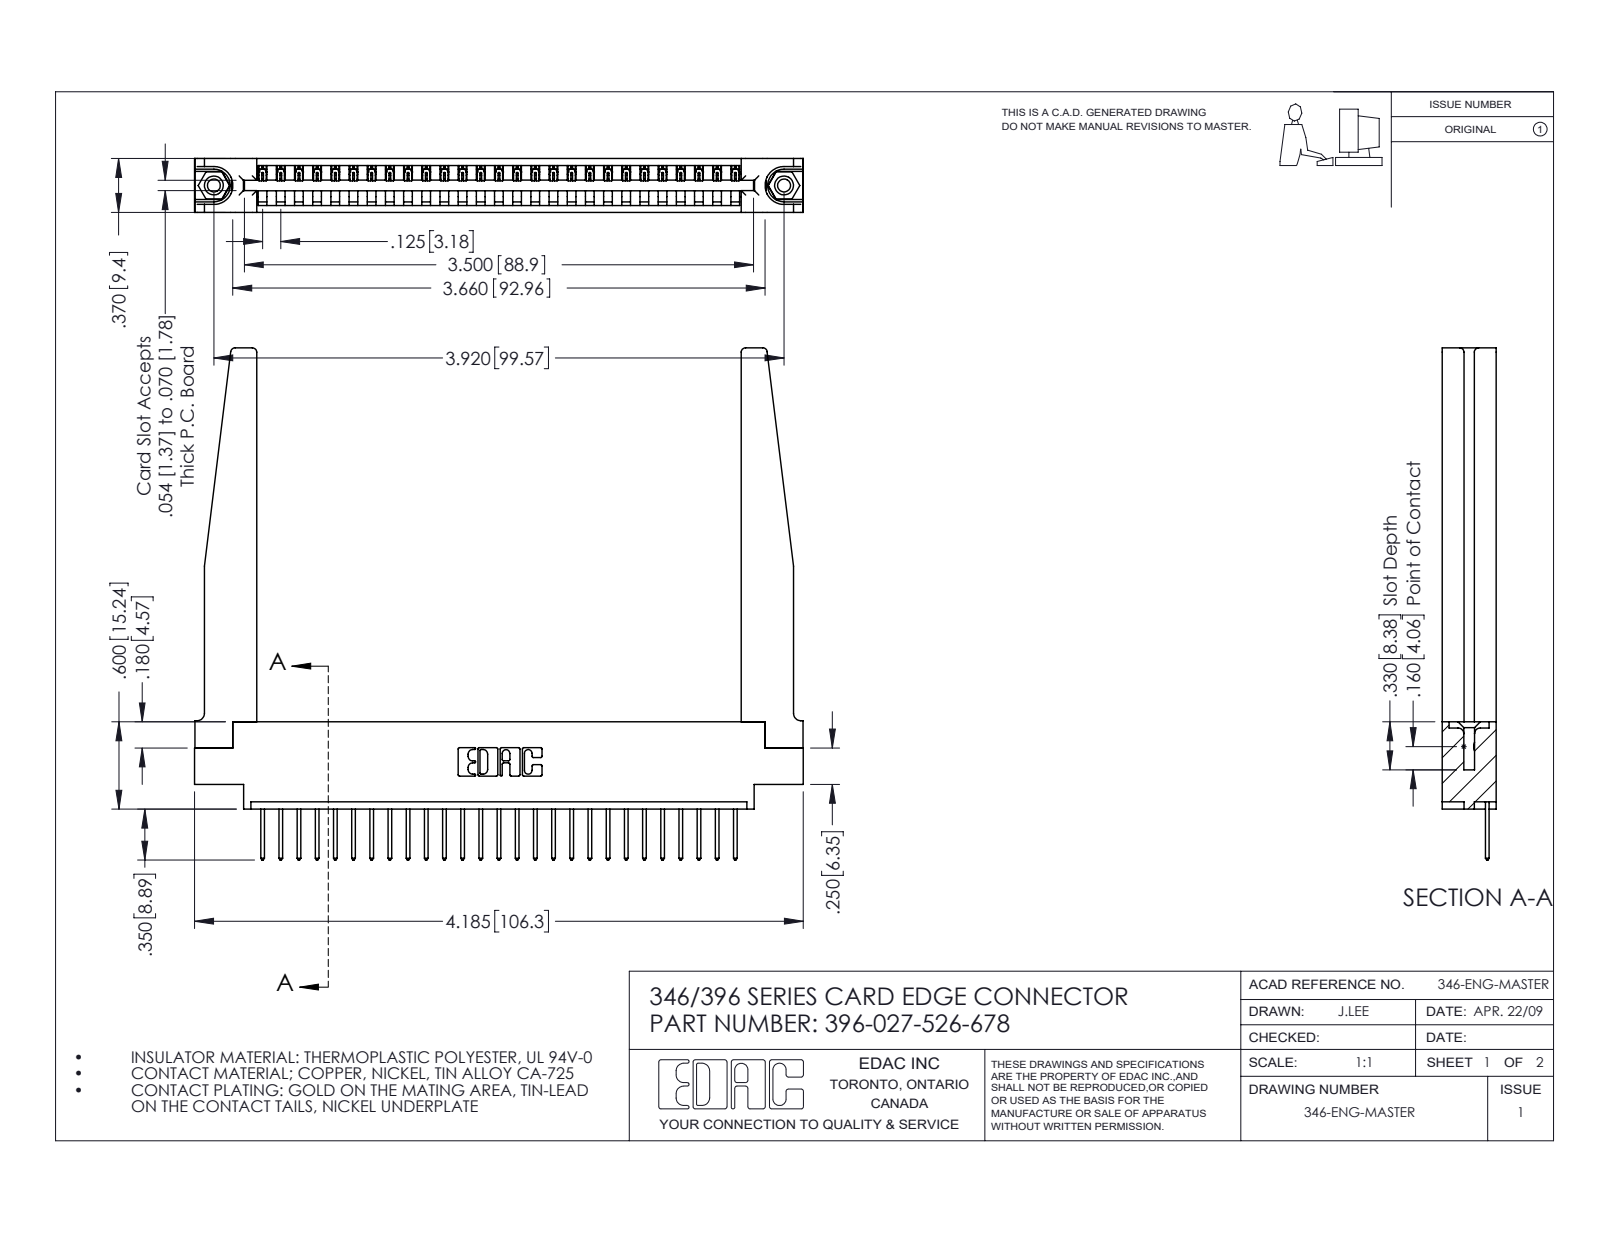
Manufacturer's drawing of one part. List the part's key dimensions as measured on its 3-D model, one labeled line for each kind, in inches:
Part name (STEP PRODUCT): 345-250-001_345-250-001-102; 396-027-526-678; 346-220-078_345-220-078; 346 Part_0.170 Offset - 0.156 Dia-TH (+1 more)
STEP written by: SolidWorks 2016 (CONFIG_CONTROL_DESIGN)
Units: inches
Bodies: 32 solids, 1926 faces (1302 planar, 572 cylindrical, 52 other)
Overall size (bounding box): 4.185 × 3.52 × 0.37
Volume: 1.025 in³ · Surface area: 29.27 in²
Round holes (diameter × count): ⌀0.089 ×2, ⌀0.125 ×2, ⌀0.156 ×2, ⌀0.064 ×1
Round bosses / shafts (diameter × count): ⌀0.155 ×2
Partial cylindrical surfaces — rounded edges, fillets, slot ends (radius × count): R0.006 ×54, R0.01 ×54, R0.01 ×22, R0.03 ×8, R0.007 ×6, R0.031 ×6, R0.026 ×3, R0.031 ×2
Main face-to-face distances: 0.37, 0.048, 0.322, 0.072, 0.148, 0.15, 0.25, 0.298, 0.025, 0.222
Hole centre spacings: 0.246, 3.712, 3.92
